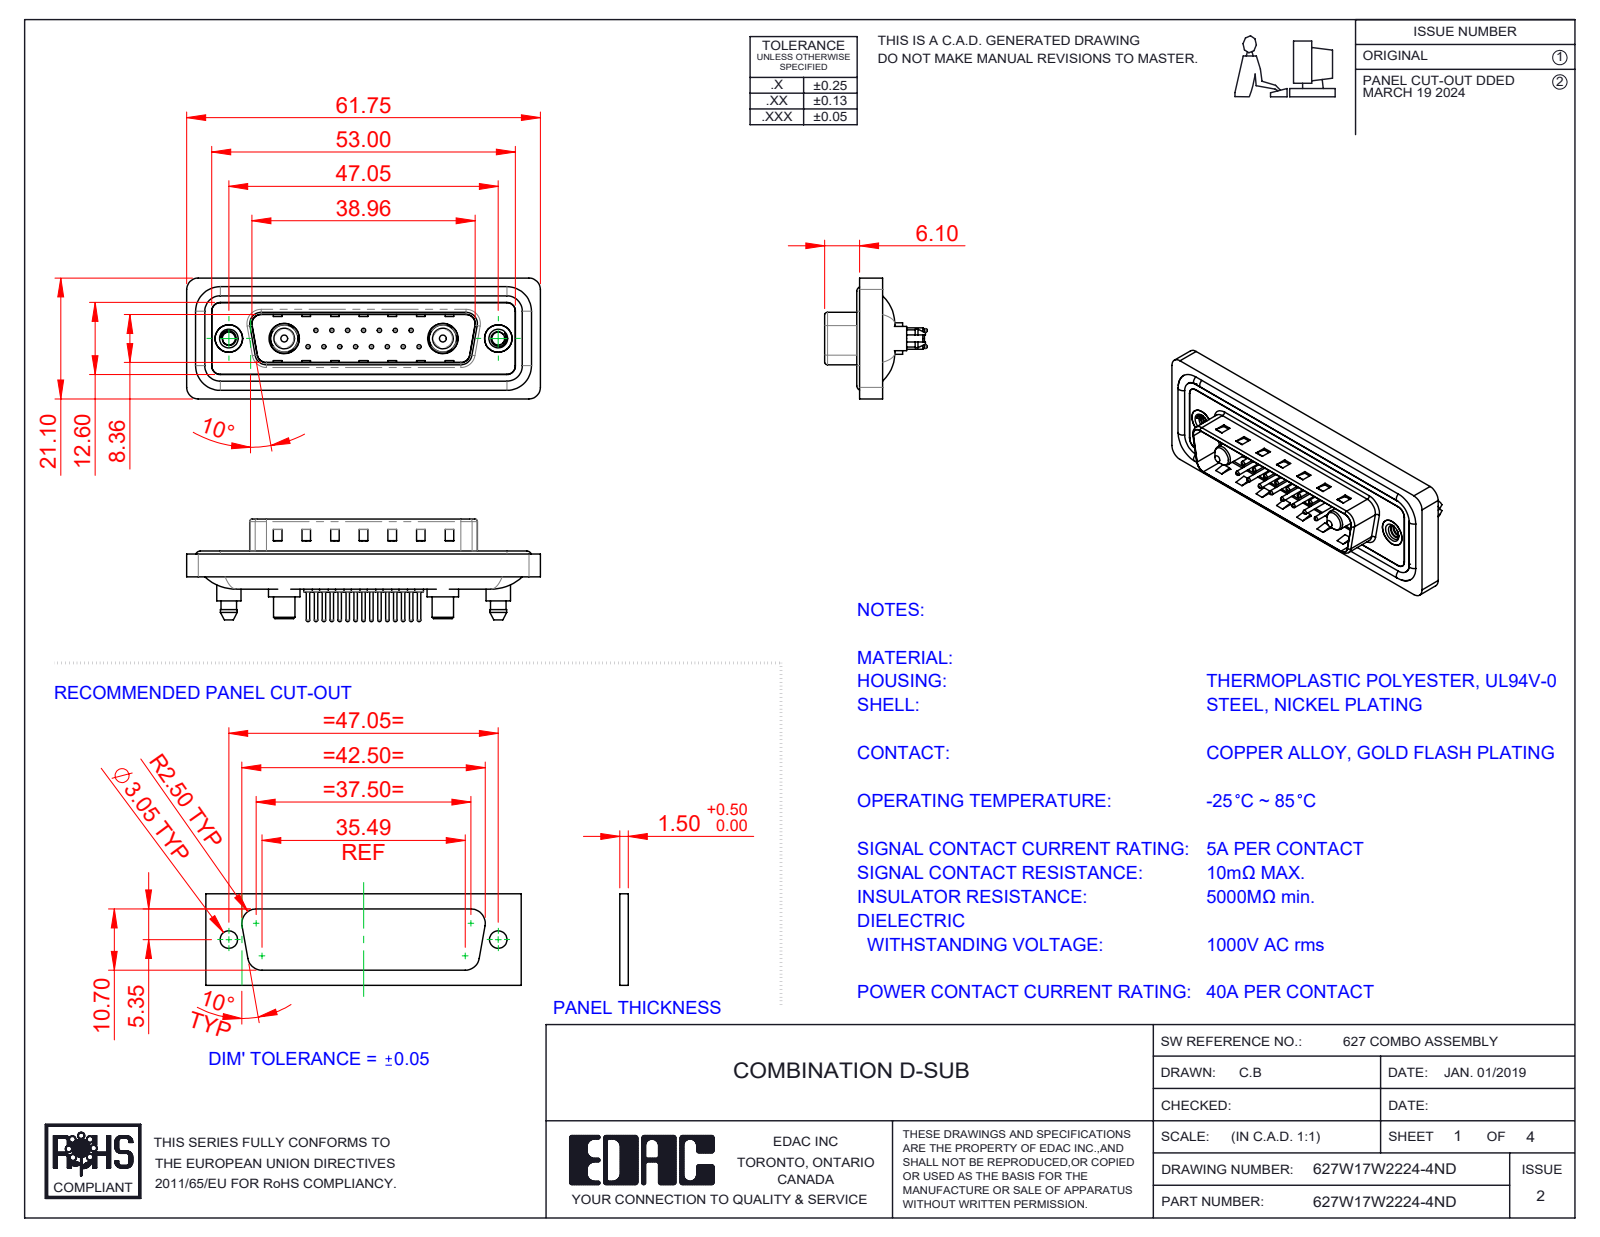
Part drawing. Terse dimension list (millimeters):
name: 627W17W2224-4ND; 627Combo Threaded Boardlock_5; 627Combo Contact Row 1_24; 627Combo Shell Front_25 Contacts (+6 more)
written by: SolidWorks 2023 (CONFIG_CONTROL_DESIGN)
unit: mm
bodies: 26 solids, 1174 faces (350 planar, 476 cylindrical, 348 other)
size: 61.75 × 21.1 × 17.9
volume: 7 438 mm³; area: 12 272 mm²
holes: 15× ⌀0.75, 15× ⌀1.6, 15× ⌀2, 2× ⌀2.26, 2× ⌀4, 2× ⌀4.8, 2× ⌀4.85, 2× ⌀5, 2× ⌀5.3
bosses: 15× ⌀1.5, 15× ⌀0.6, 4× ⌀1.6, 2× ⌀5.5, 2× ⌀5.4, 2× ⌀5.2, 2× ⌀4.9, 2× ⌀4.75
rounds: 24× R1.5, 18× R2, 10× R1.6, 8× R0.5, 4× R0.25, 4× R0.6, 4× R0.65, 4× R0.9
face distances: 0.4, 1.5, 1.1, 1.6, 0.5, 3.1, 2.9, 0.82, 9.58, 4.1
hole spacings: 3.16, 2.77, 5.54, 8.31, 5.04, 7.49, 11.08, 5.03
